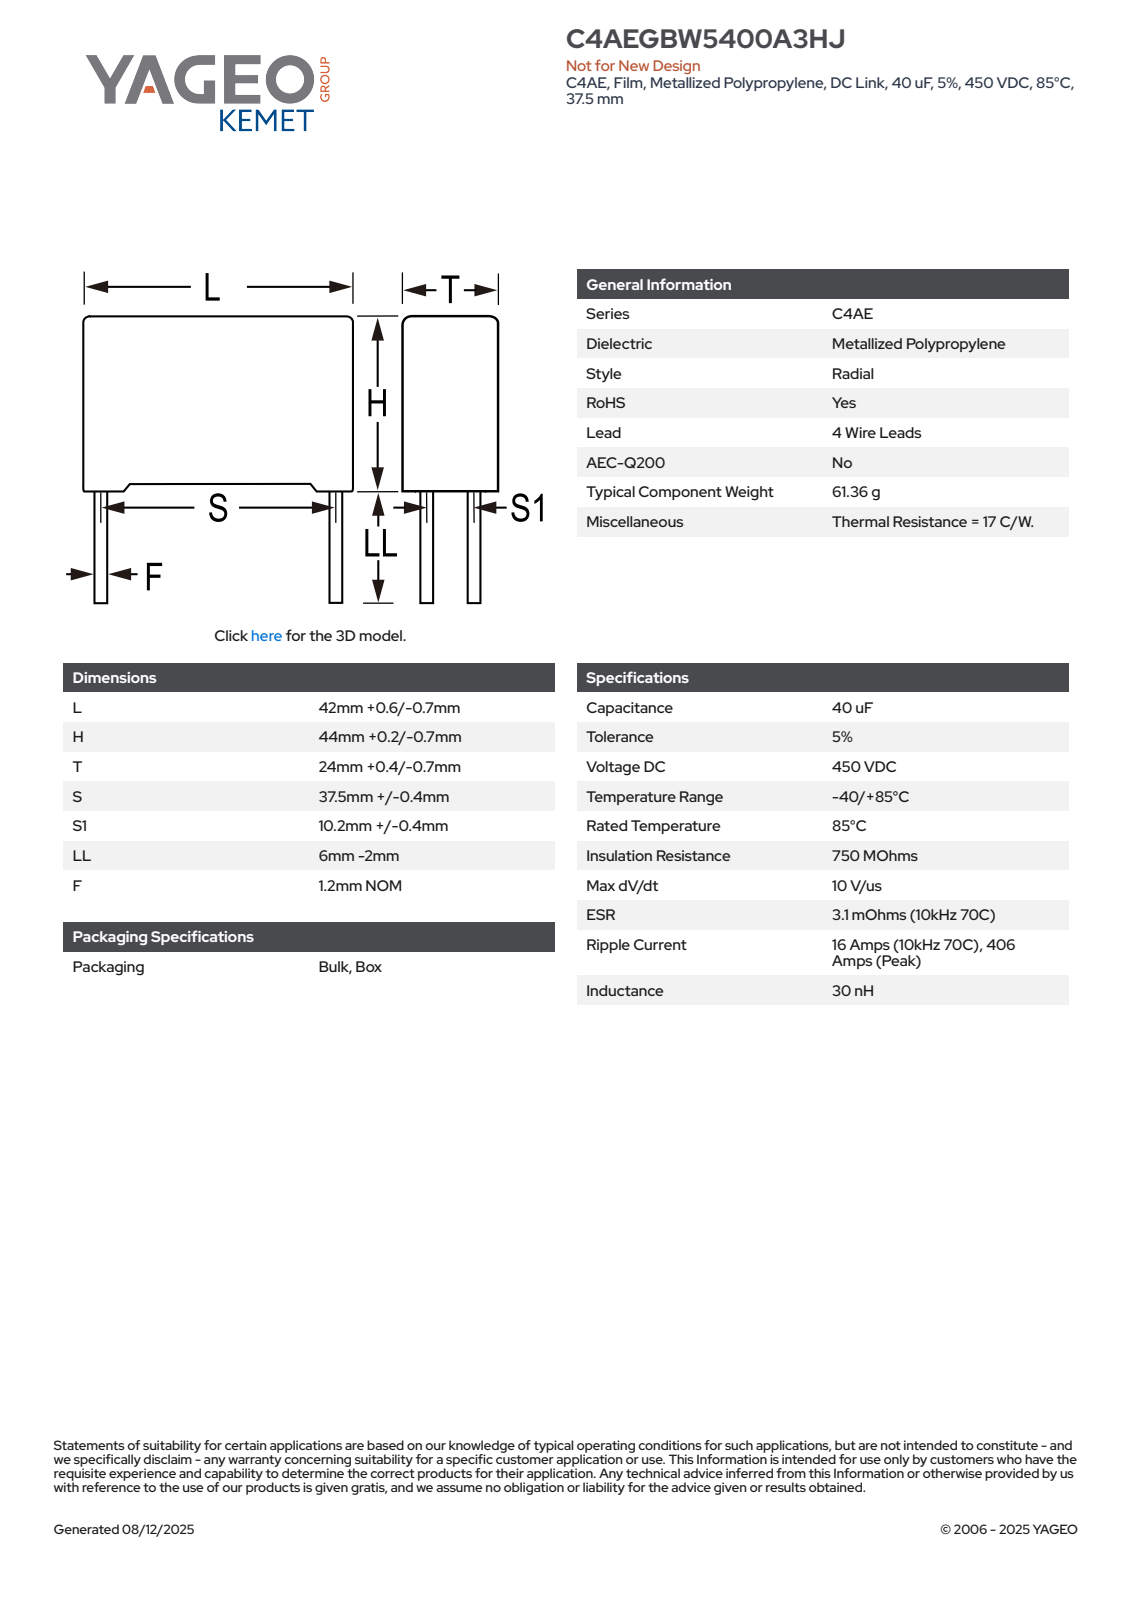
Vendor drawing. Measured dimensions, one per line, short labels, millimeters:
name: CFP_RB4_41.5X44X24_L42.6H44.2T24.4S37.5S110.2LL4F1.2
written by: SolidWorks 2014 (AUTOMOTIVE_DESIGN)
unit: mm
bodies: 4 solids, 87 faces (79 planar, 8 cylindrical, 0 other)
size: 48.2 × 42.6 × 24.41
volume: 44 758 mm³; area: 8 217 mm²
bosses: 4× ⌀1.2
face distances: 24.4, 42.6, 42.9, 1.3, 44.2, 1.5, 24.41, 41.1, 22.9, 39.6
